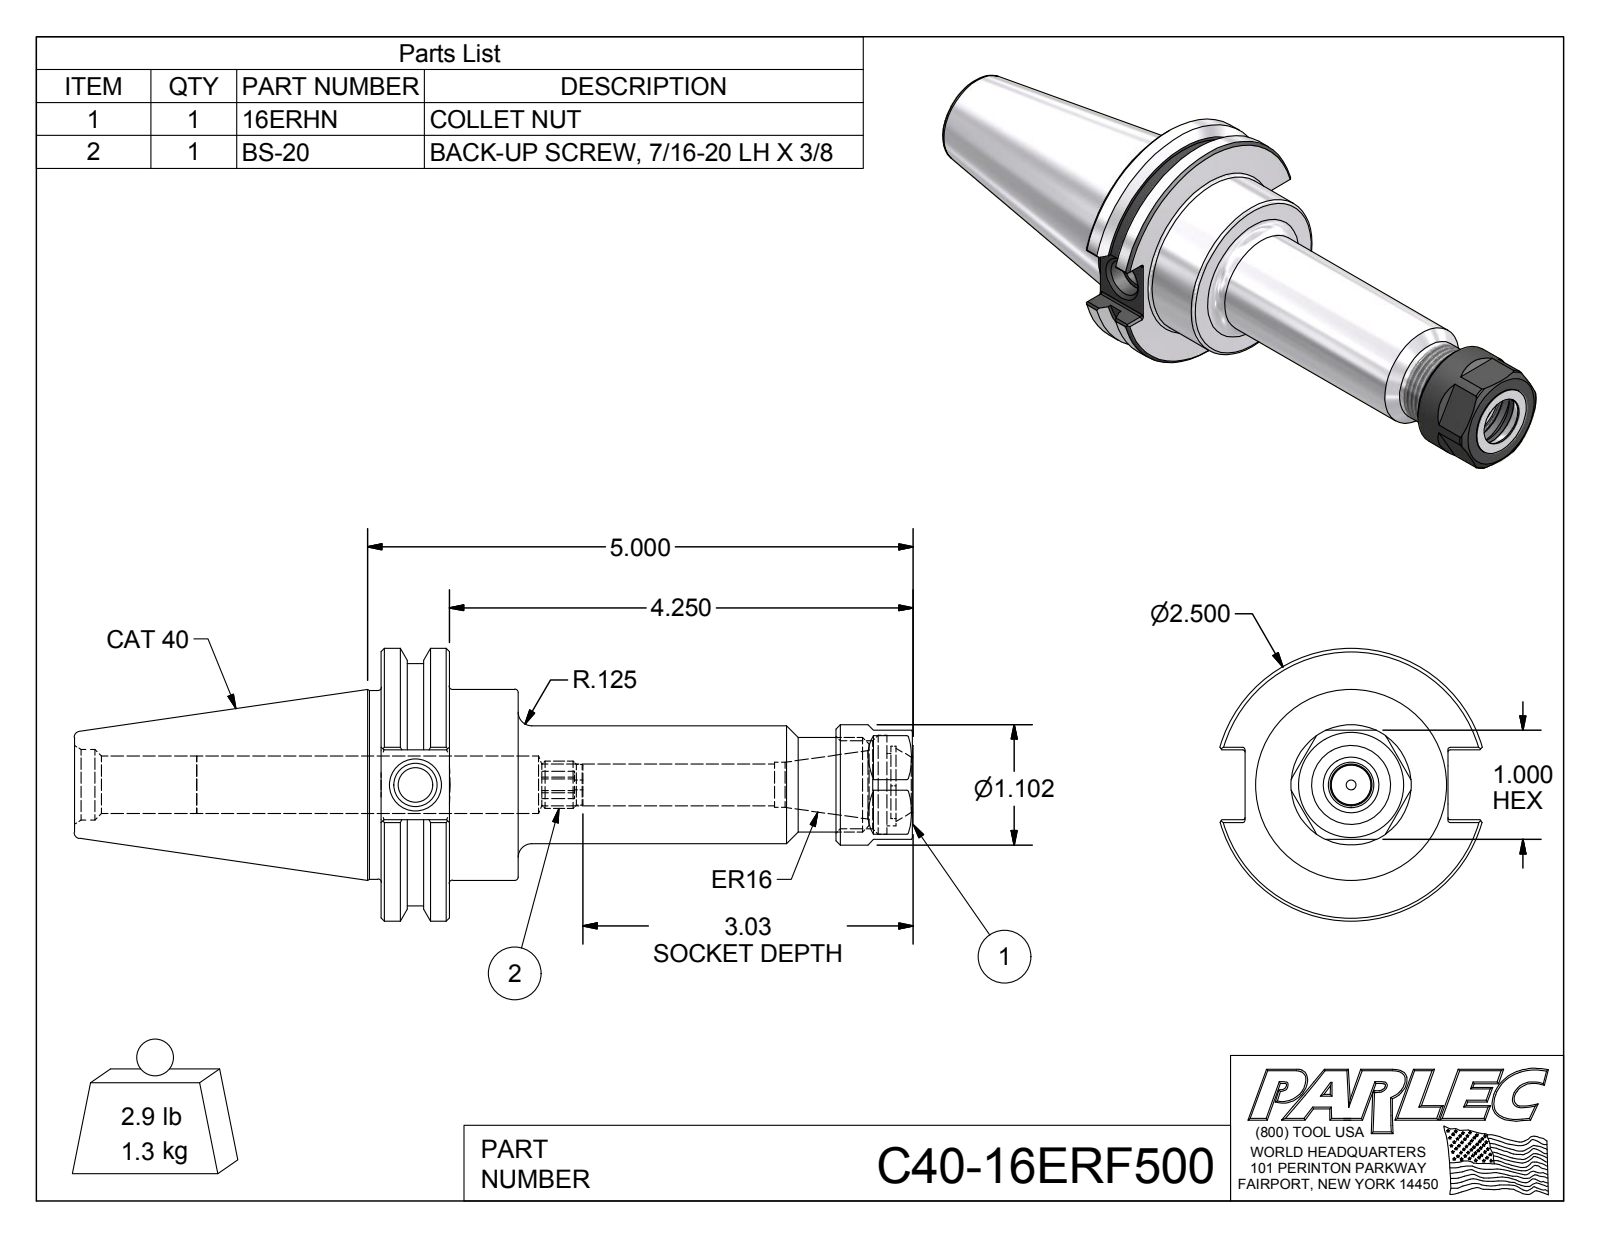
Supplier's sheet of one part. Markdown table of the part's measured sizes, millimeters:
| quantity | value |
| --- | --- |
| part name | C40-16ER5-1; BS-20; 16ERHN; C40-16ERF500 |
| STEP written by | Autodesk Inventor 2016 (AUTOMOTIVE_DESIGN) |
| units | millimeters |
| bodies | 3 solids, 137 faces (59 planar, 39 cylindrical, 39 other) |
| overall size | 195.26 × 63.5 × 61.05 |
| volume | 165 226 mm³ |
| surface area | 36 397 mm² |
| round holes (diameter × count) | 2.29 × 1, 8 × 1, 9.73 × 1, 10.13 × 1, 10.5 × 1, 12.4 × 1, 13.38 × 1, 13.39 × 1, 16.46 × 1, 17.02 × 1, 20.5 × 1, 23 × 1 |
| round bosses / shafts (diameter × count) | 63.5 × 1, 56.36 × 1, 44.45 × 1, 43.94 × 1, 28 × 1, 27.43 × 1, 22 × 1, 10.97 × 1 |
| partial cylindrical surfaces (radius × count) | 0.51 × 12, 7.24 × 1, 9 × 1 |
| main face-to-face distances | 15.88, 31.88, 16, 123.83, 107.95, 91.95, 25.14, 20.7, 4.44, 118.13 |
| hole center spacings | 1.52 |
